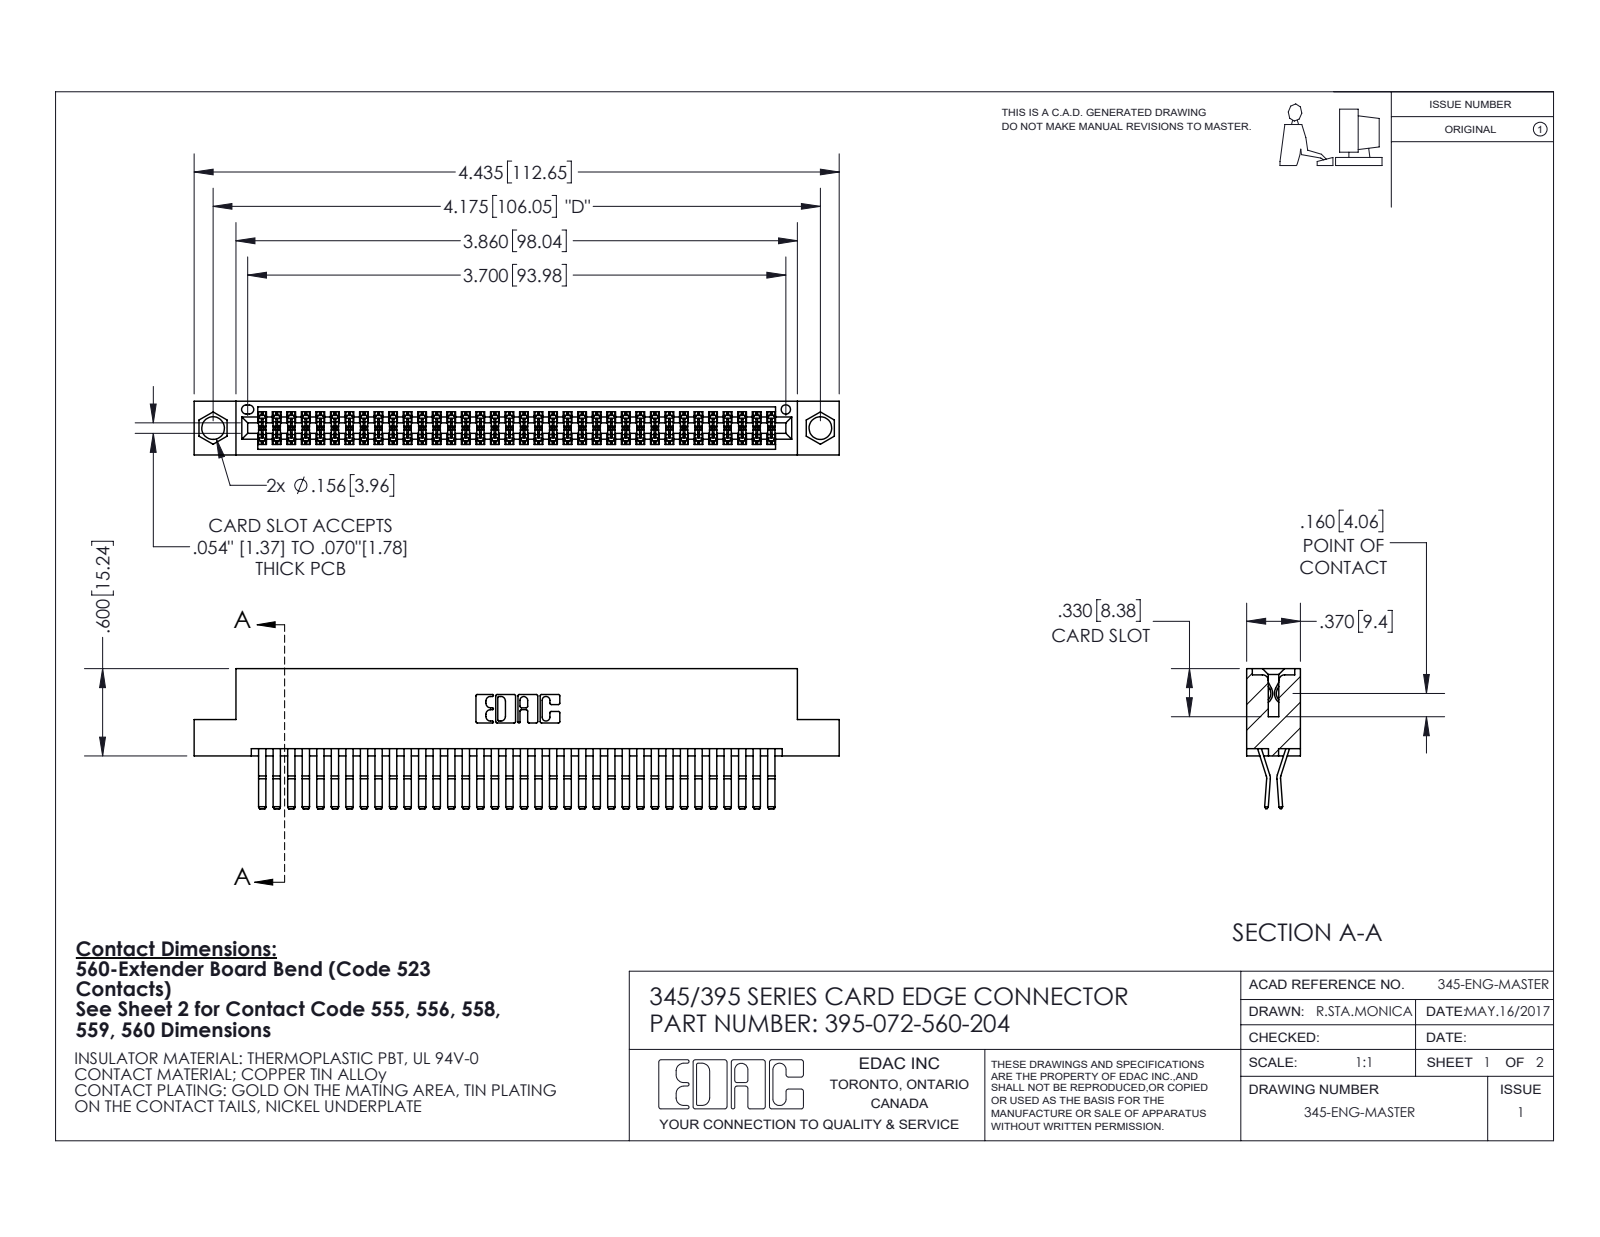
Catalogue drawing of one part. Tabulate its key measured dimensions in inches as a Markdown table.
| quantity | value |
| --- | --- |
| part name | 345 Part_Flush Mounting Lugs - 0.156 Dia-TI; 395-072-560-204; 345-292-001_560 Tail |
| STEP written by | SolidWorks 2020 (CONFIG_CONTROL_DESIGN) |
| units | inches |
| bodies | 73 solids, 3884 faces (2470 planar, 1414 cylindrical, 0 other) |
| overall size | 4.435 × 0.962 × 0.37 |
| volume | 0.687 in³ |
| surface area | 27.25 in² |
| round holes (diameter × count) | 0.156 × 2, 0.064 × 1 |
| partial cylindrical surfaces (radius × count) | 0.006 × 108, 0.01 × 22, 0.007 × 6, 0.031 × 6, 0.026 × 3, 0.01 × 2, 0.014 × 2, 0.019 × 2 |
| main face-to-face distances | 0.025, 0.298, 0.072, 0.37, 0.2, 0.098, 0.272, 0.225, 0.175, 0.149 |
| hole center spacings | 0.27, 3.939, 4.175 |
